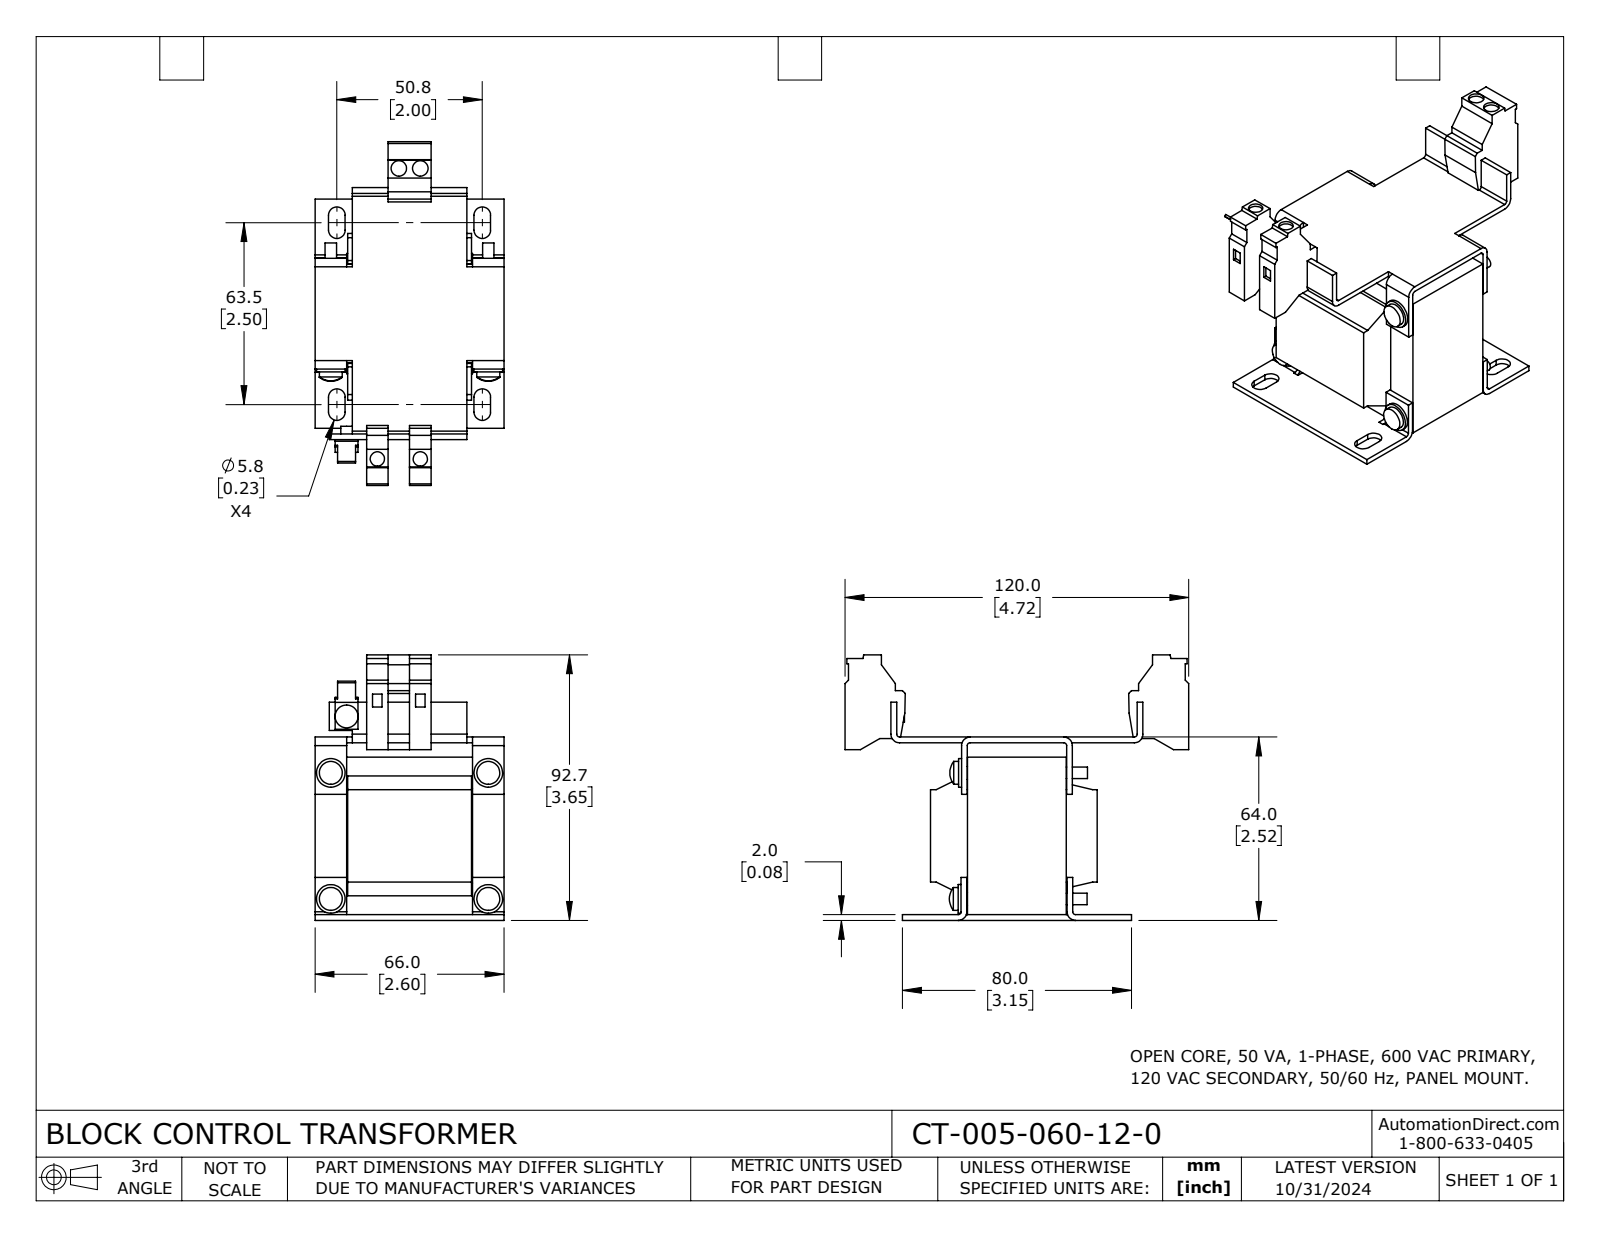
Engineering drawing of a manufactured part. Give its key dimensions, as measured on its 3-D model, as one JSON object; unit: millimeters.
{"part_name": "CT-005-060-12-0", "step_written_by": "SolidWorks 2023 (CONFIG_CONTROL_DESIGN)", "units": "millimeters", "bodies": {"solids": 1, "faces": 326, "planar": 233, "cylindrical": 89, "other": 4}, "overall_size": [120, 92.7, 66], "volume_mm3": 198900, "surface_area_mm2": 54990, "round_holes": [[5, 2], [5.4, 2]], "round_bosses_or_shafts": [[8, 5], [4, 5], [10, 4], [4.5, 4]], "partial_cylinders_radius": [[2.9, 8], [1, 6], [3, 6]], "face_to_face_distances": [2, 62, 55, 11, 64, 11.4, 54.6, 60, 44, 7], "hole_center_spacings": [101.7, 7.5, 15, 101.4, 102.5]}
